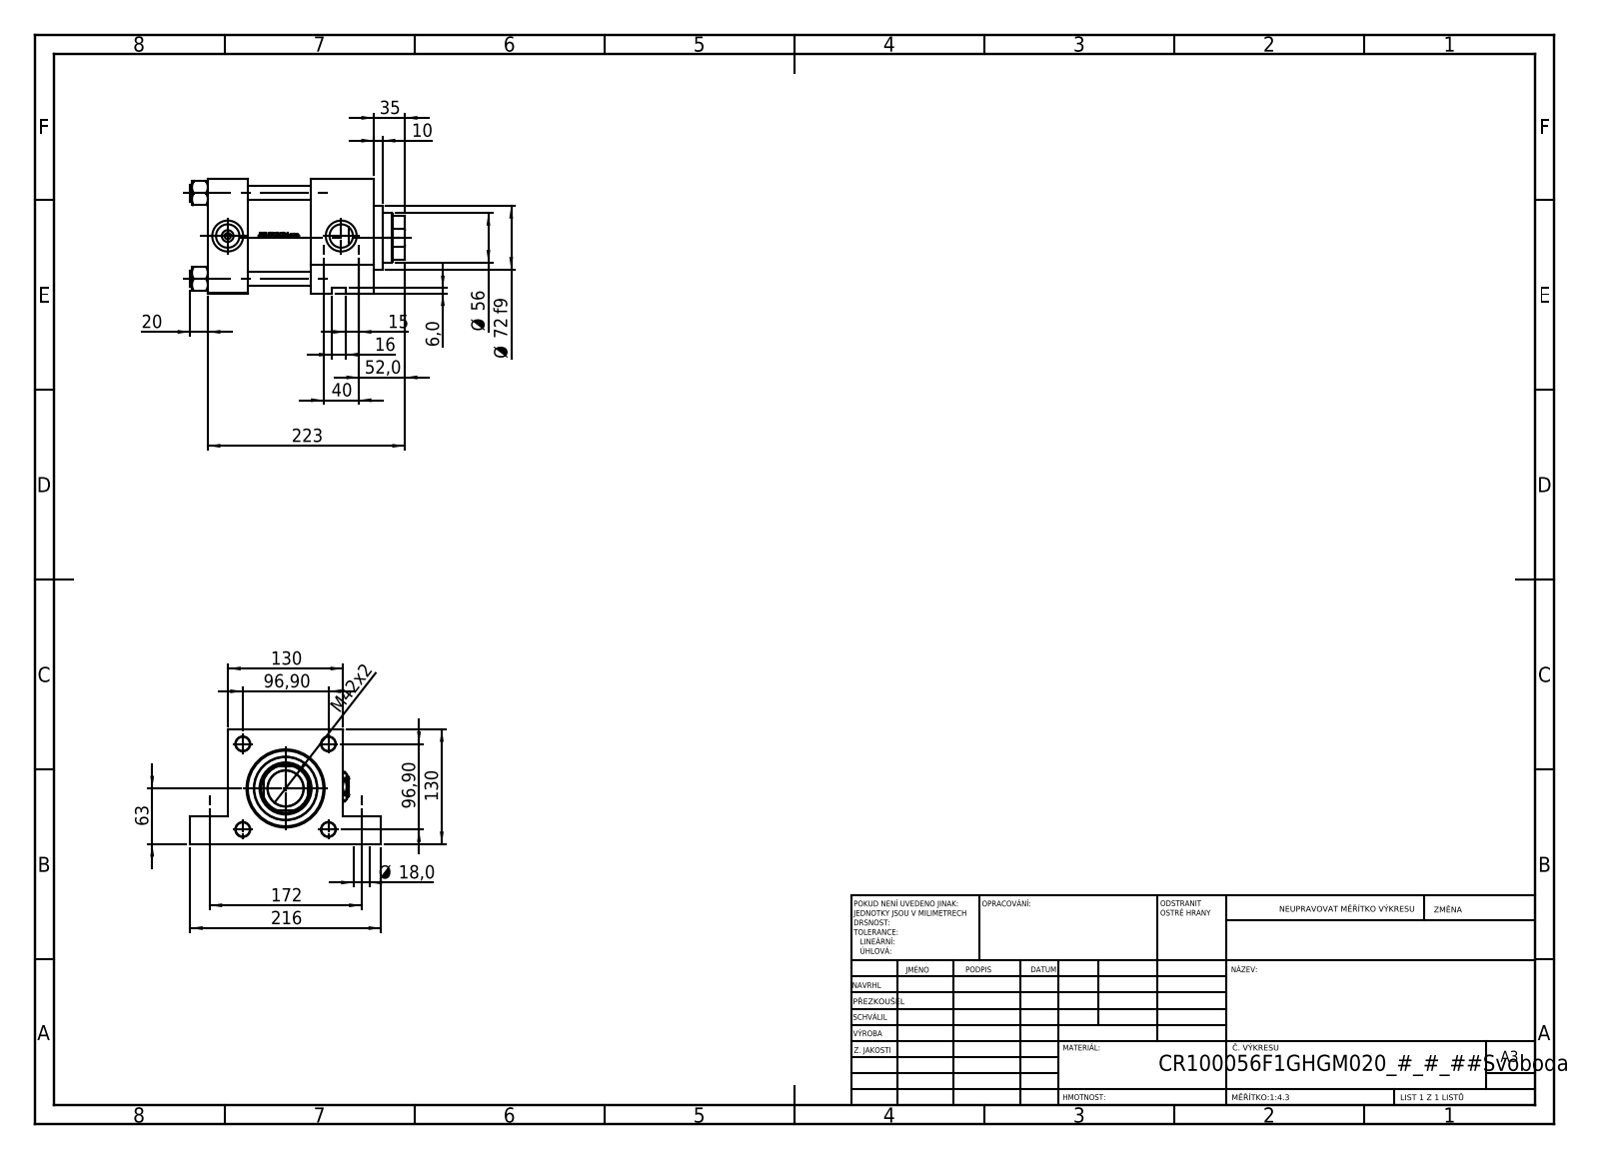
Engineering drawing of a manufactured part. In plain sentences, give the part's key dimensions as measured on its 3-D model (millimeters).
The part is named "NUT_M5_F; V215CR_F_Body; V215_VC_A; Zatka_pro_OIL_PORT (+2 more)". Its 3-D file was written by "SolidWorks 2019 (CONFIG_CONTROL_DESIGN)". It is 12 solids with 1198 faces: 508 planar, 130 cylindrical and 560 other. Overall it measures 243 by 216 by 130 millimeters. Its volume is 2 624 000 cubic millimeters and its surface area 358 147 square millimeters. Round holes: 4 of diameter 16, 4 of diameter 18, 3 of diameter 26.44, 3 of diameter 35, 2 of diameter 7, 1 of diameter 40.5, 1 of diameter 56, 1 of diameter 59, 1 of diameter 76, 1 of diameter 85.5, 1 of diameter 100. Round bosses or shafts: 4 of diameter 19, 1 of diameter 106, 1 of diameter 72. Partial cylindrical surfaces (rounded edges, fillets, slot ends): 1 of radius 27. The main face-to-face distances are 130, 45, 188, 143, 116, 71, 72, 20, 32, 92. The hole center spacings are 96.9, 40, 67.12, 69.95, 137.04, 172, 176.59, 10.
